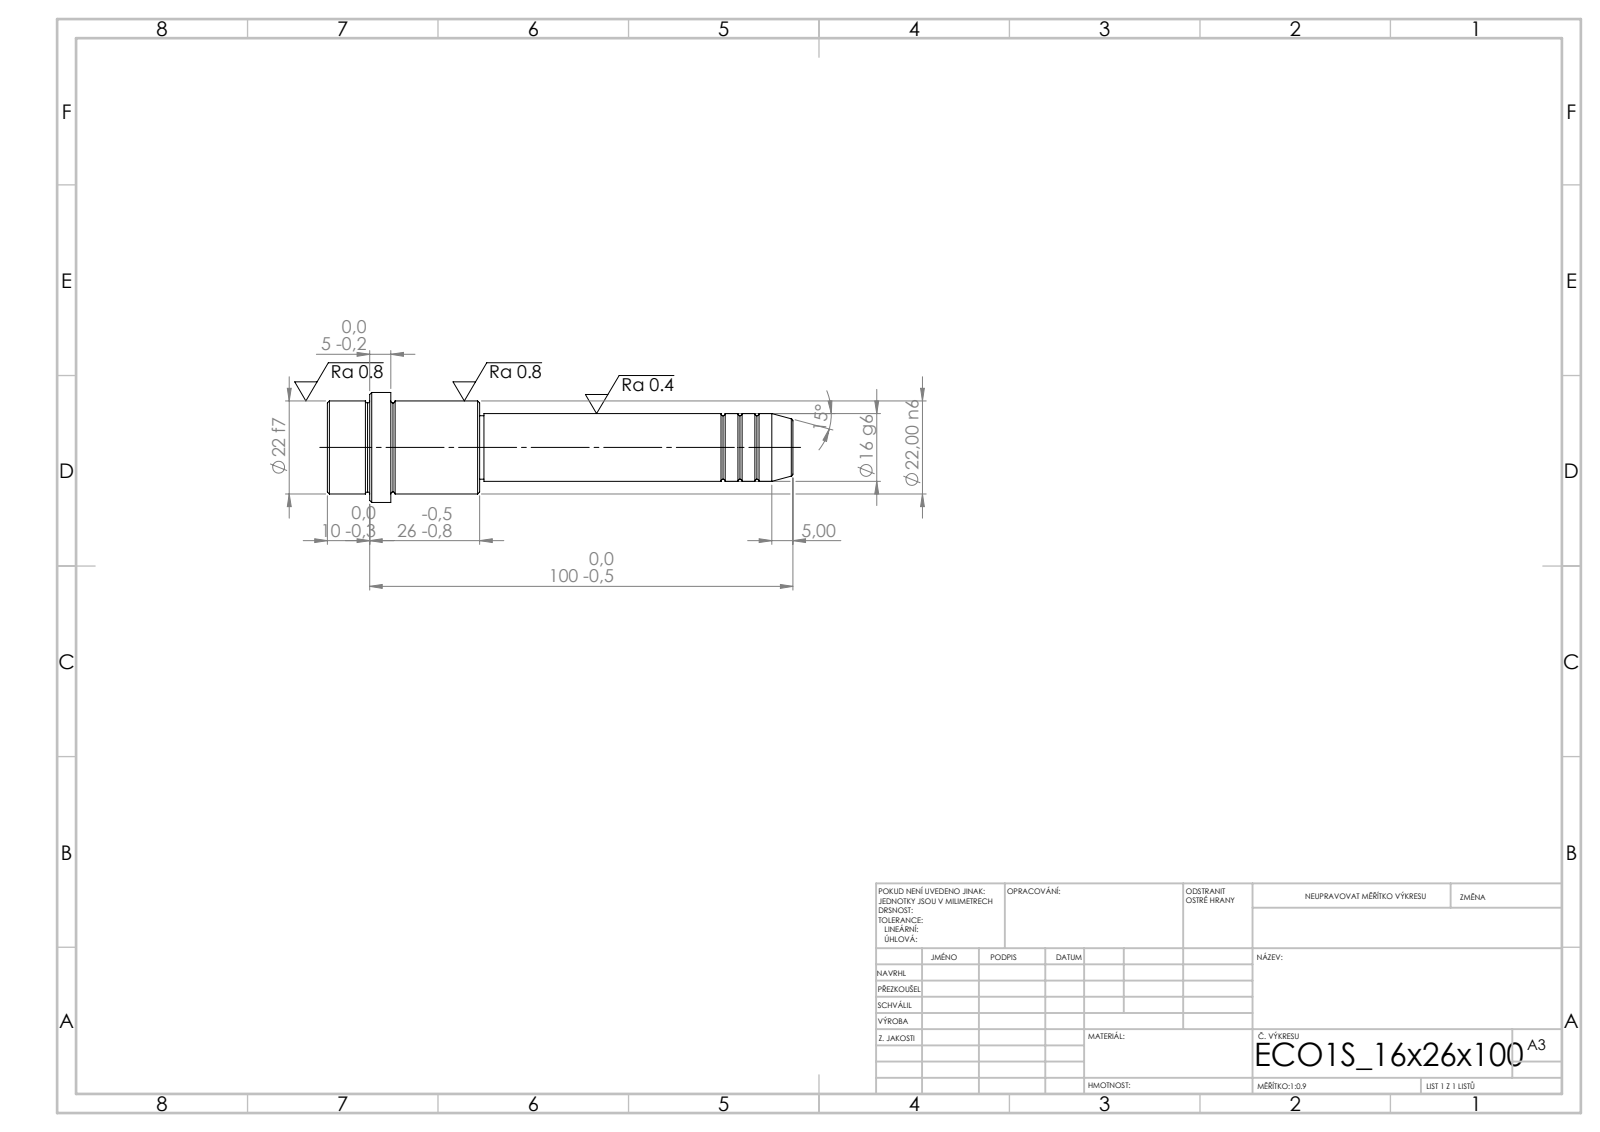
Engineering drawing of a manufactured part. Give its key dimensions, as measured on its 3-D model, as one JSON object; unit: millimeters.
{"step_written_by": "SolidWorks 2019 (CONFIG_CONTROL_DESIGN)", "units": "millimeters", "bodies": {"solids": 1, "faces": 52, "planar": 6, "cylindrical": 16, "other": 30}, "overall_size": [110, 26, 26], "volume_mm3": 28995, "surface_area_mm2": 7382, "round_bosses_or_shafts": [[26, 1], [22, 1], [16, 1], [15, 1]], "face_to_face_distances": [36, 21, 15, 74, 95, 110, 100, 26, 5, 10]}
